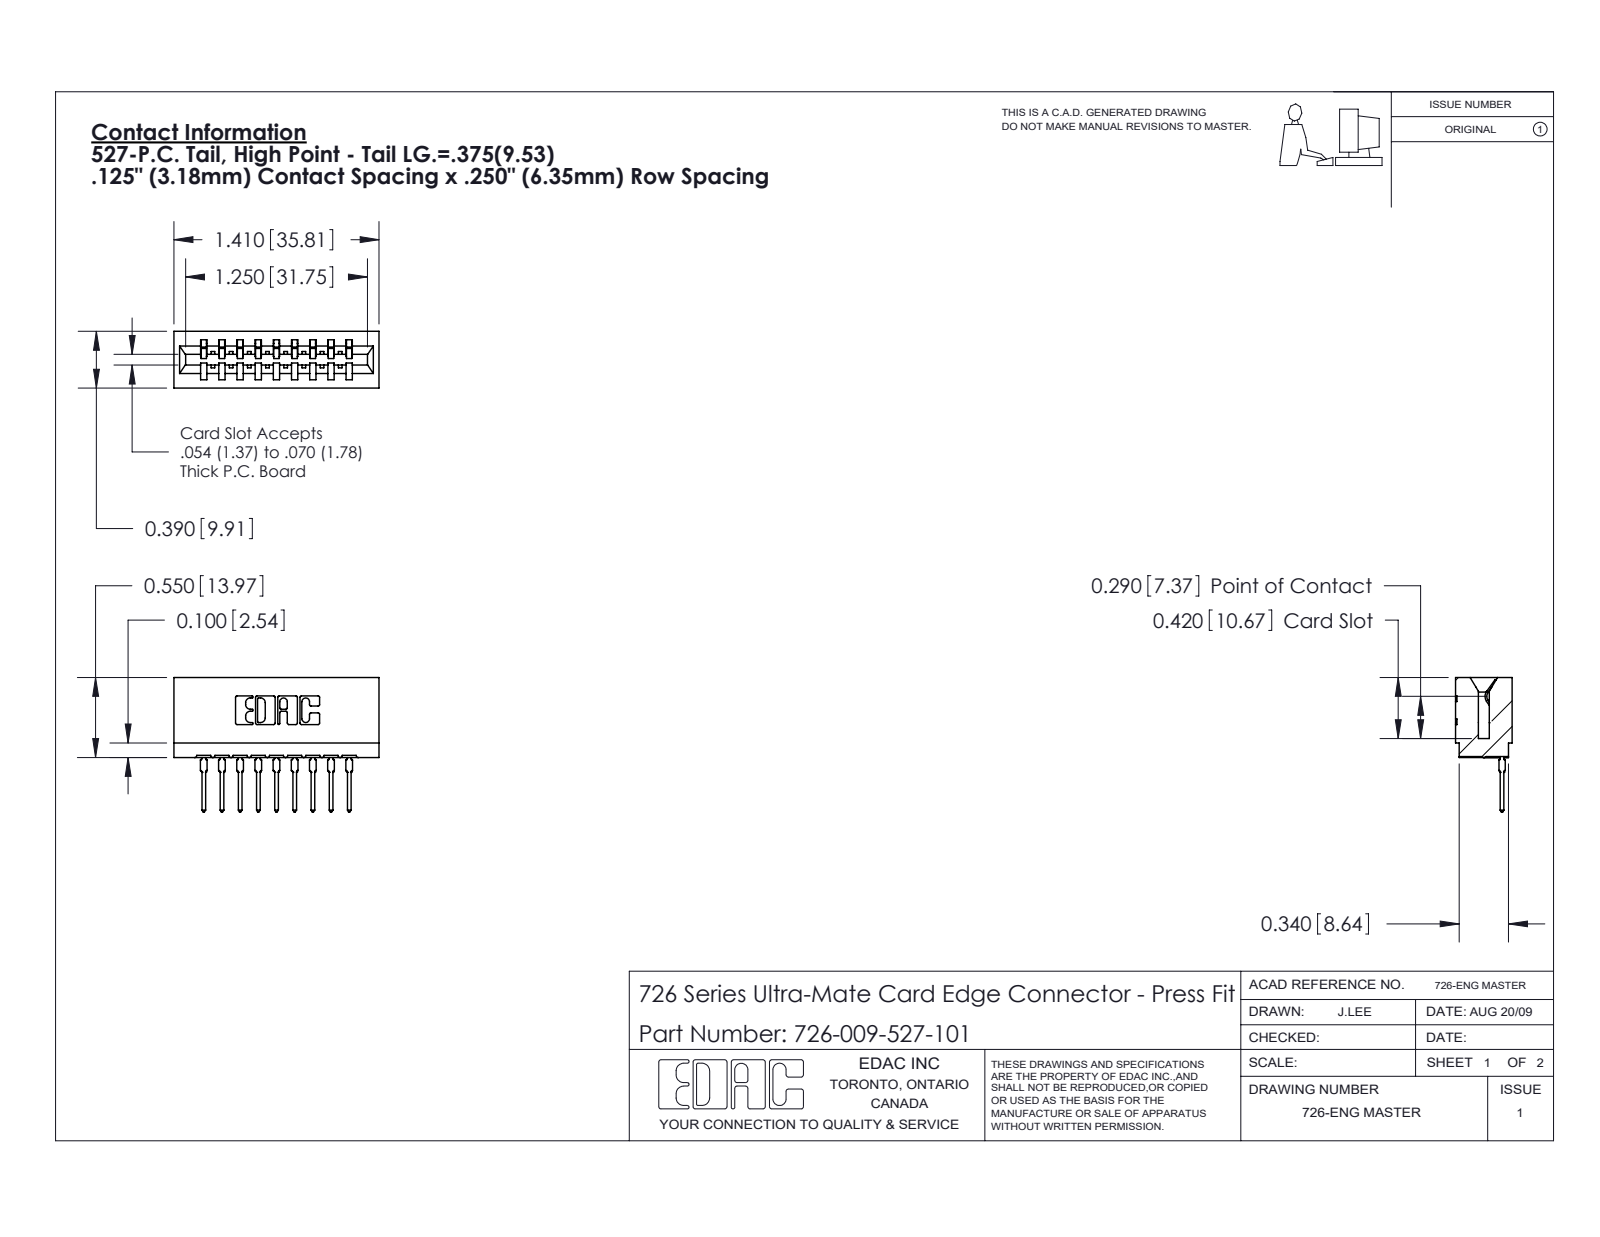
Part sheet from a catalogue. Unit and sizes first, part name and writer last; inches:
Units: inches
Overall size (bounding box): 1.41 × 0.924 × 0.39
Partial cylindrical surfaces — rounded edges, fillets, slot ends (radius × count): R0.01 ×22, R0.021 ×18, R0.015 ×10, R0.007 ×6, R0.031 ×6, R0.005 ×4, R0.011 ×4, R0.026 ×3
Main face-to-face distances: 0.25, 0.5, 0.333, 0.042, 0.125, 0.125, 0.057, 0.208, 0.292, 0.75
Volume: 0.207 in³ · Surface area: 7.359 in²
Bodies: 10 solids, 1069 faces (622 planar, 213 cylindrical, 234 other)
Part name (STEP PRODUCT): 726-009-527-101; 726 Part_.515 Slot Depth - 01; 746-292-001_527
STEP written by: SolidWorks 2020 (CONFIG_CONTROL_DESIGN)
